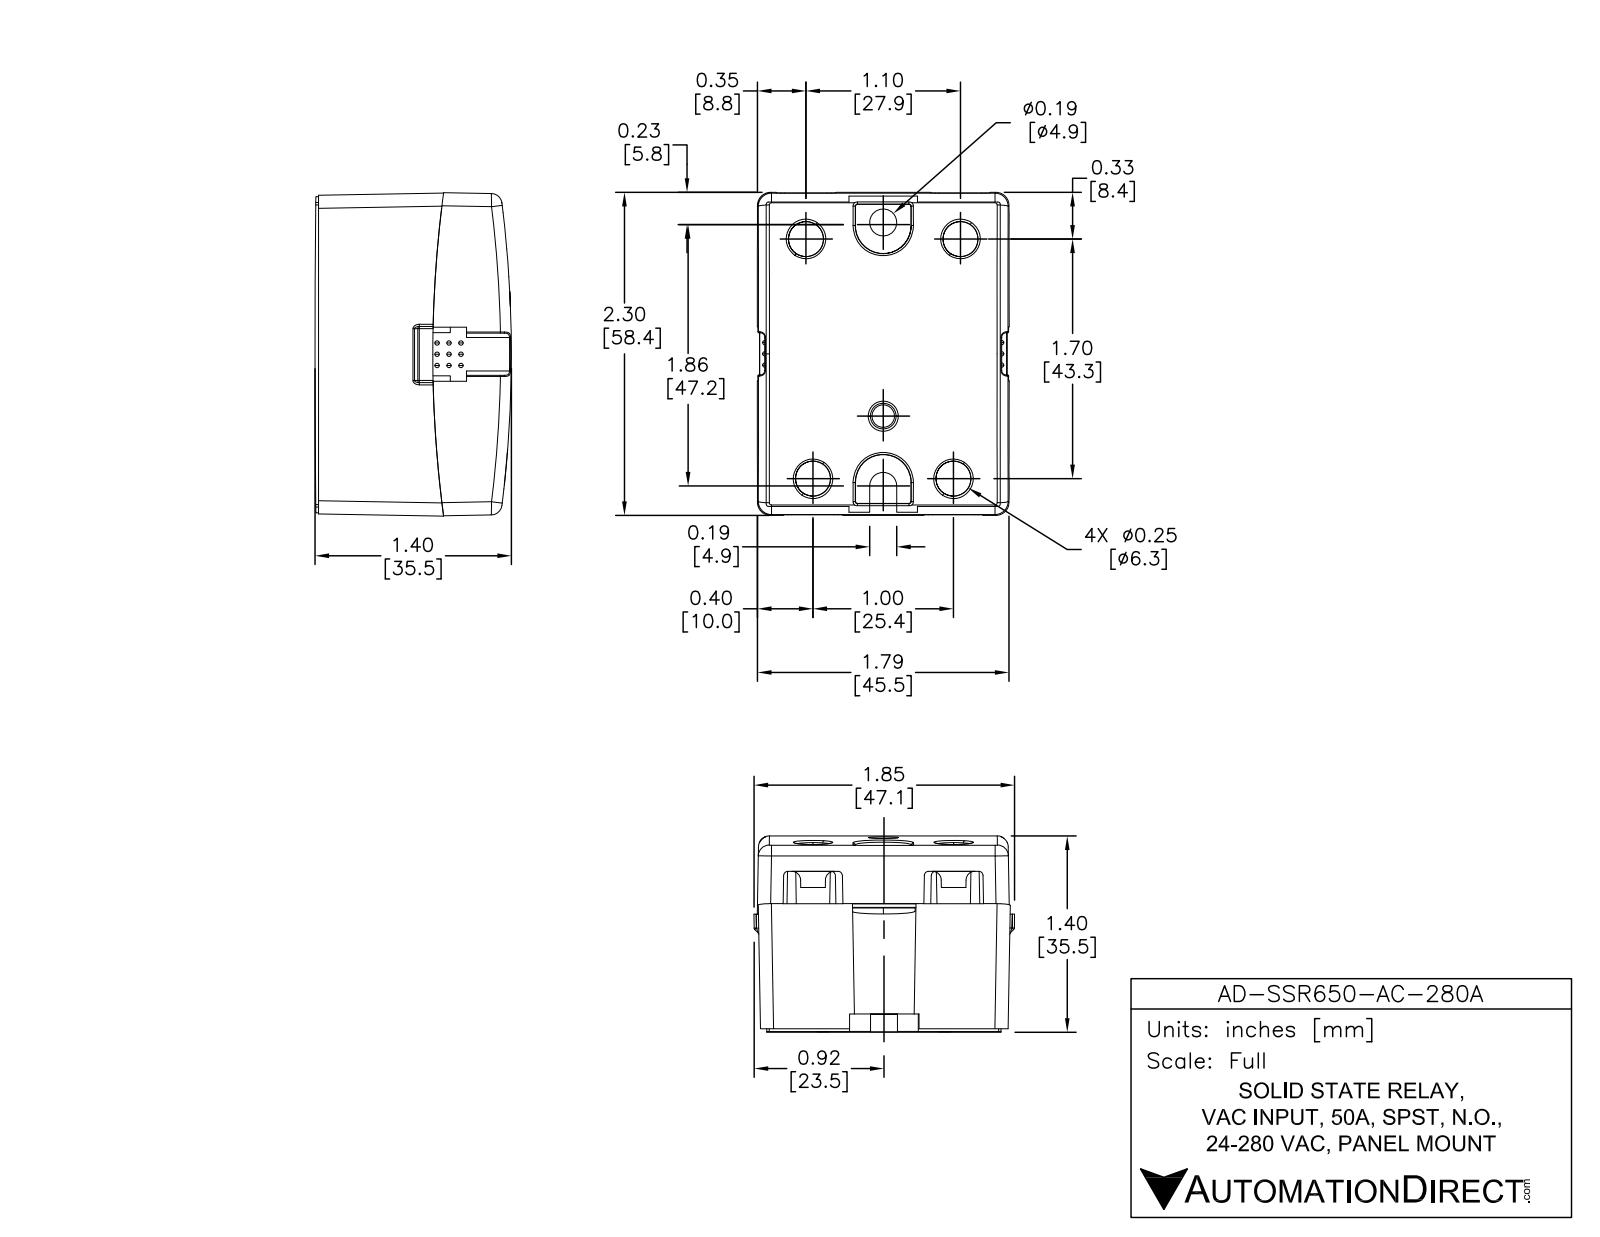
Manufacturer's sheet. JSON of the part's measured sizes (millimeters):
{"part_name": "AD-SSR650-AC-280A", "step_written_by": "SolidWorks 2013 (AUTOMOTIVE_DESIGN)", "units": "millimeters", "bodies": {"solids": 3, "faces": 251, "planar": 145, "cylindrical": 95, "other": 11}, "overall_size": [58.4, 45.5, 35.6], "volume_mm3": 84230, "surface_area_mm2": 17040, "round_holes": [[6.4, 4], [4.8, 1]], "round_bosses_or_shafts": [[10.2, 2], [8.9, 2], [7.6, 2], [6.4, 2], [5.1, 2], [5.1, 2]], "partial_cylinders_radius": [[0.8, 6], [0.3, 4], [1, 4], [12.7, 4], [4.9, 2], [2.4, 1], [12.7, 1], [12.7, 1]], "face_to_face_distances": [45.5, 58.4, 29.6, 6.4, 23.3, 17, 26.9, 12.7, 45.7, 2], "hole_center_spacings": [14.1, 14.4, 25.4, 27.9, 43.2, 43.2, 47.7, 47.7]}
